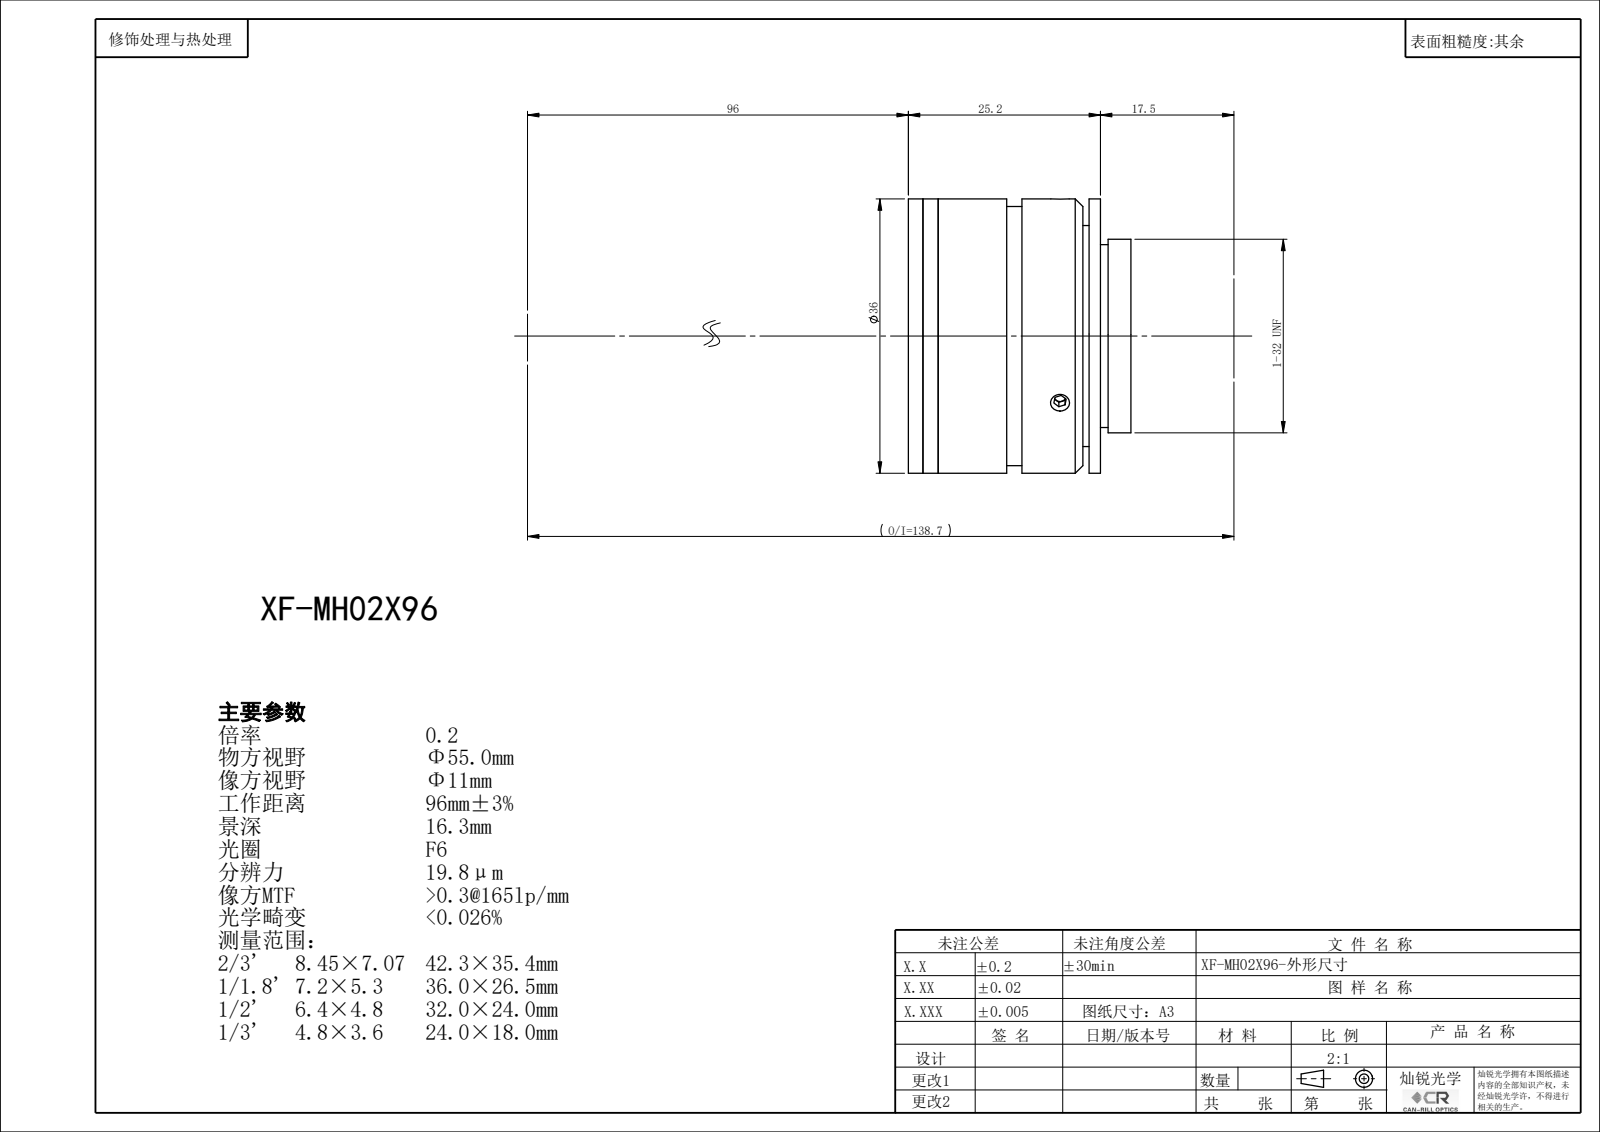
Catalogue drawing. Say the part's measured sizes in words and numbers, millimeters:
The part is named "XF-MH02X96". Its 3-D file was written by "SolidWorks 2022 (CONFIG_CONTROL_DESIGN)". It is 0 solids with 113 faces: 53 planar, 50 cylindrical and 10 other. Overall it measures 36 by 36 by 29.23 millimeters. Round holes: 3 of diameter 2.5, 1 of diameter 7, 1 of diameter 8.4, 1 of diameter 10, 1 of diameter 12, 1 of diameter 14, 1 of diameter 16, 1 of diameter 18, 1 of diameter 20, 1 of diameter 21.5, 1 of diameter 22, 1 of diameter 24. Round bosses or shafts: 1 of diameter 36, 1 of diameter 34, 1 of diameter 25.4, 1 of diameter 9. The main face-to-face distances are 2, 3.91, 1.91, 23.32, 21.32, 25.23, 4, 1, 1.5, 23.73.
